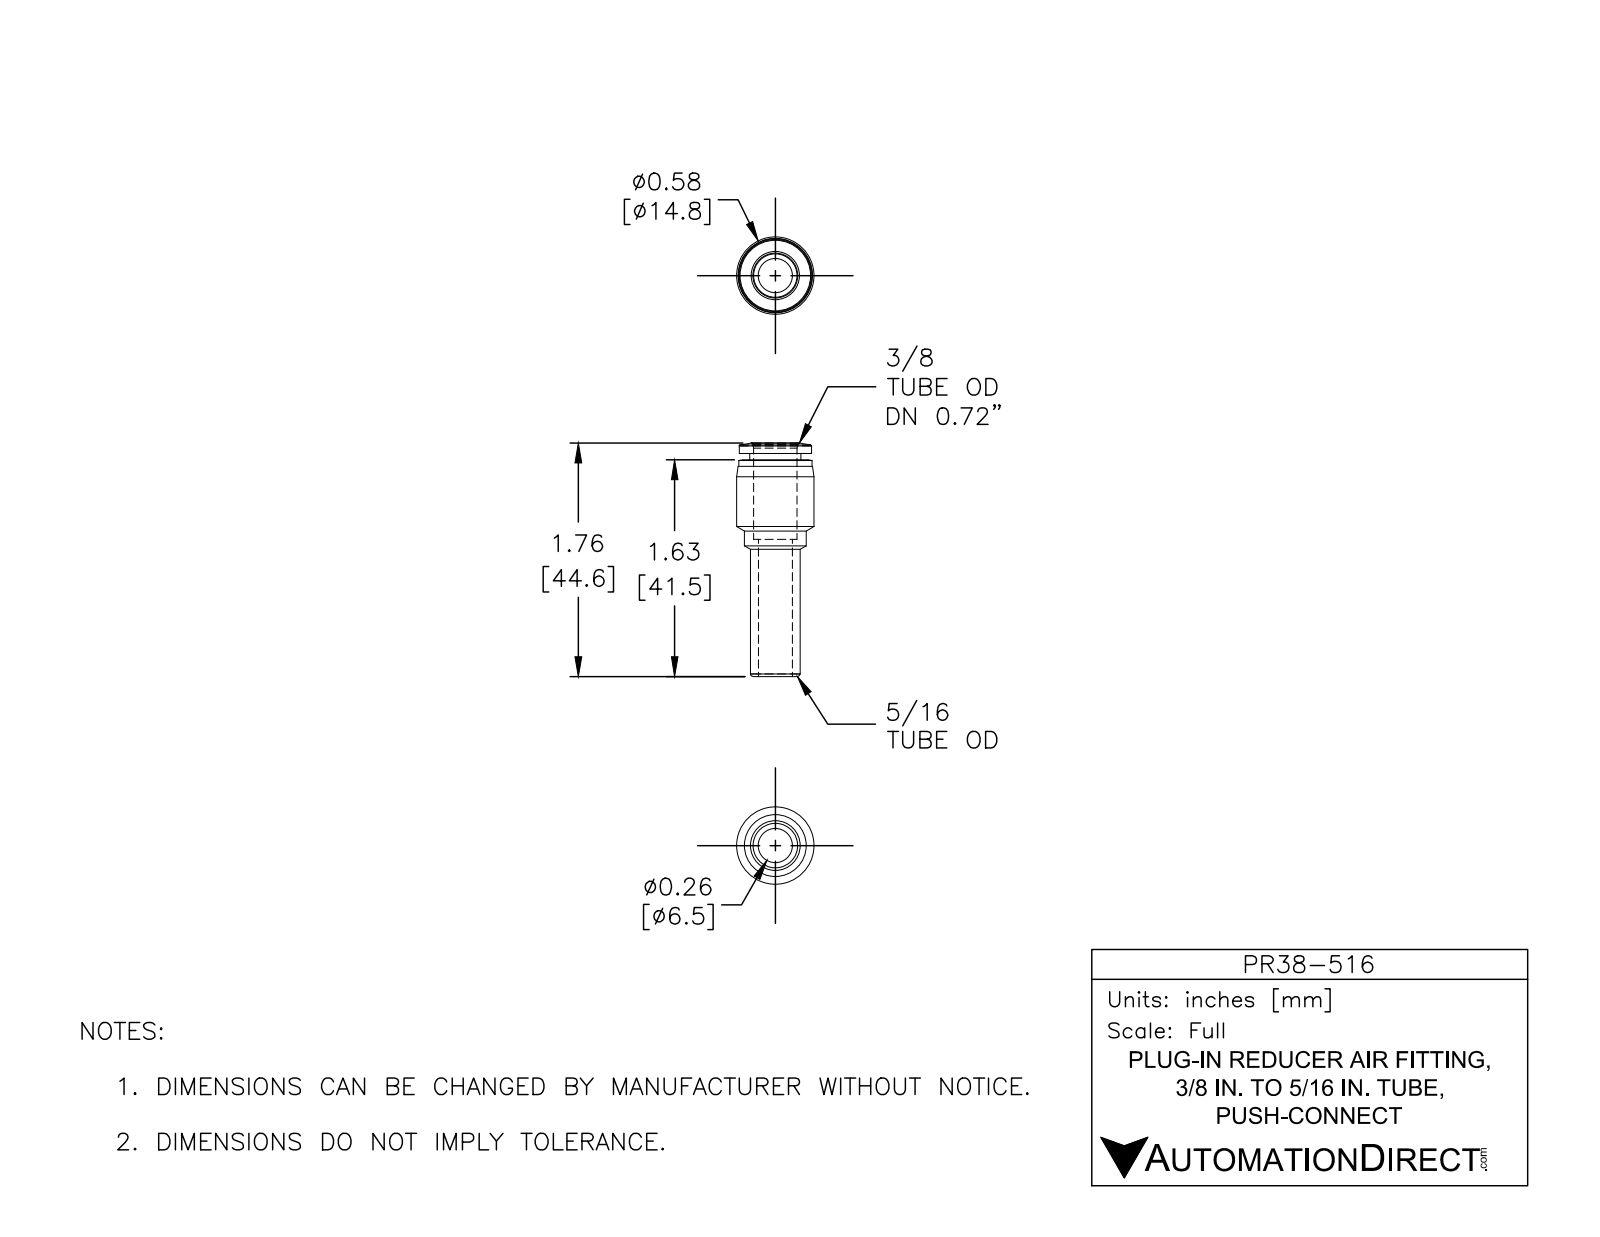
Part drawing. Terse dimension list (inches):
name: PR38-516
written by: SolidWorks 2015 (CONFIG_CONTROL_DESIGN)
unit: in
bodies: 1 solid, 39 faces (5 planar, 16 cylindrical, 18 other)
size: 1.758 × 0.583 × 0.583
volume: 0.175 in³; area: 4.574 in²
holes: 1× ⌀0.256, 1× ⌀0.327
bosses: 1× ⌀0.583, 1× ⌀0.551, 1× ⌀0.543, 1× ⌀0.465, 1× ⌀0.386, 1× ⌀0.374
face distances: 0.047, 1.632, 1.679, 1.033, 0.598, 0.646, 1.583, 0.549, 0.049, 0.096
